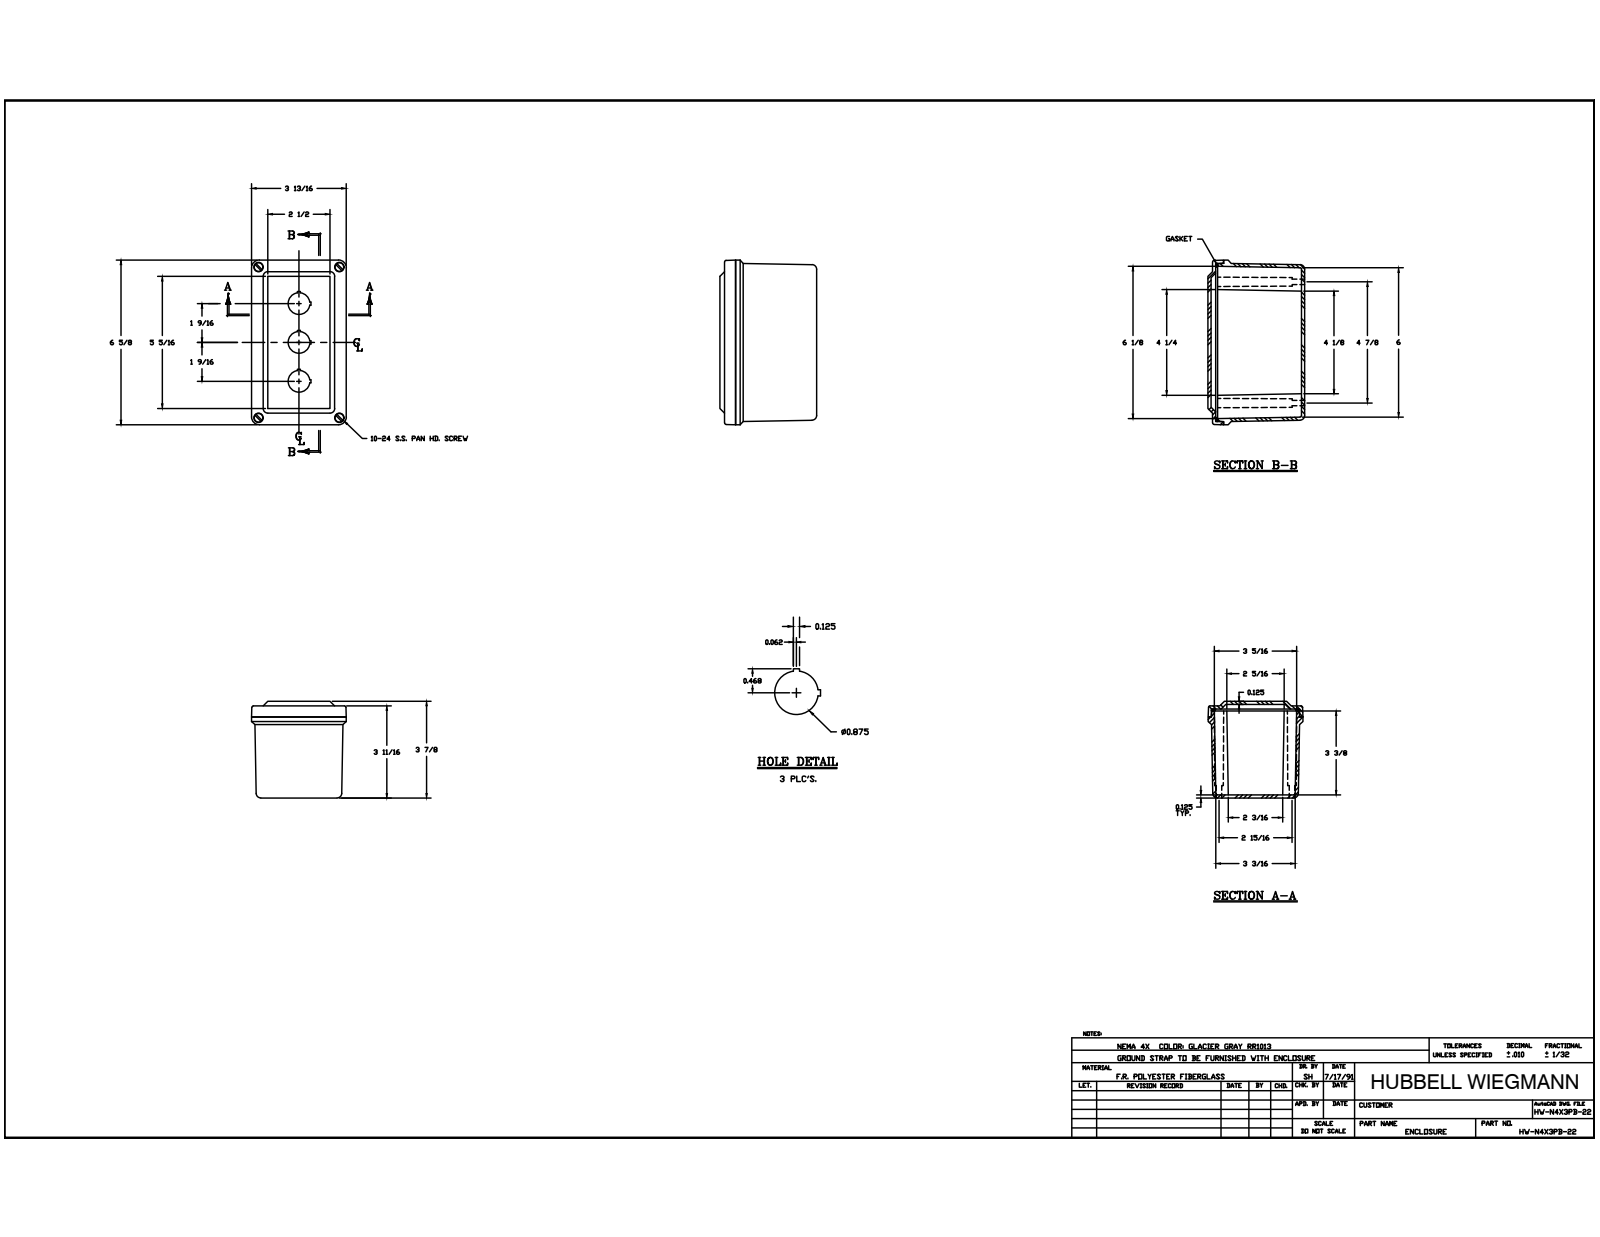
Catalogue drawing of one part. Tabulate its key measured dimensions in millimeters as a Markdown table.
| quantity | value |
| --- | --- |
| part name | WPCF644 BOX; 10-24 X 0.4375 DP BRASS INSERT; WPCF3PB22 CVR; WPCF644 GASKET (+3 more) |
| STEP written by | Autodesk Inventor 2014 (AUTOMOTIVE_DESIGN) |
| units | millimeters |
| bodies | 11 solids, 403 faces (201 planar, 110 cylindrical, 92 other) |
| overall size | 168.28 × 98.42 × 96.84 |
| volume | 332 459 mm³ |
| surface area | 171 051 mm² |
| round holes (diameter × count) | 5.56 × 8, 3.68 × 4, 4.83 × 4, 9.52 × 4, 22.22 × 3 |
| round bosses / shafts (diameter × count) | 9.42 × 4, 5.54 × 4, 4.5 × 4 |
| partial cylindrical surfaces (radius × count) | 0.79 × 20, 0.3 × 16, 7.94 × 8, 1.59 × 4, 4.47 × 4, 4.76 × 4, 5.59 × 4, 8.26 × 4 |
| main face-to-face distances | 3.17, 3.42, 95.25, 4.76, 90.49, 12.7, 98.42, 1.59, 92.08, 87.32 |
| hole center spacings | 15.59, 43.43, 55.63, 72.28, 80.01, 87.35, 108.23, 123.76 |
